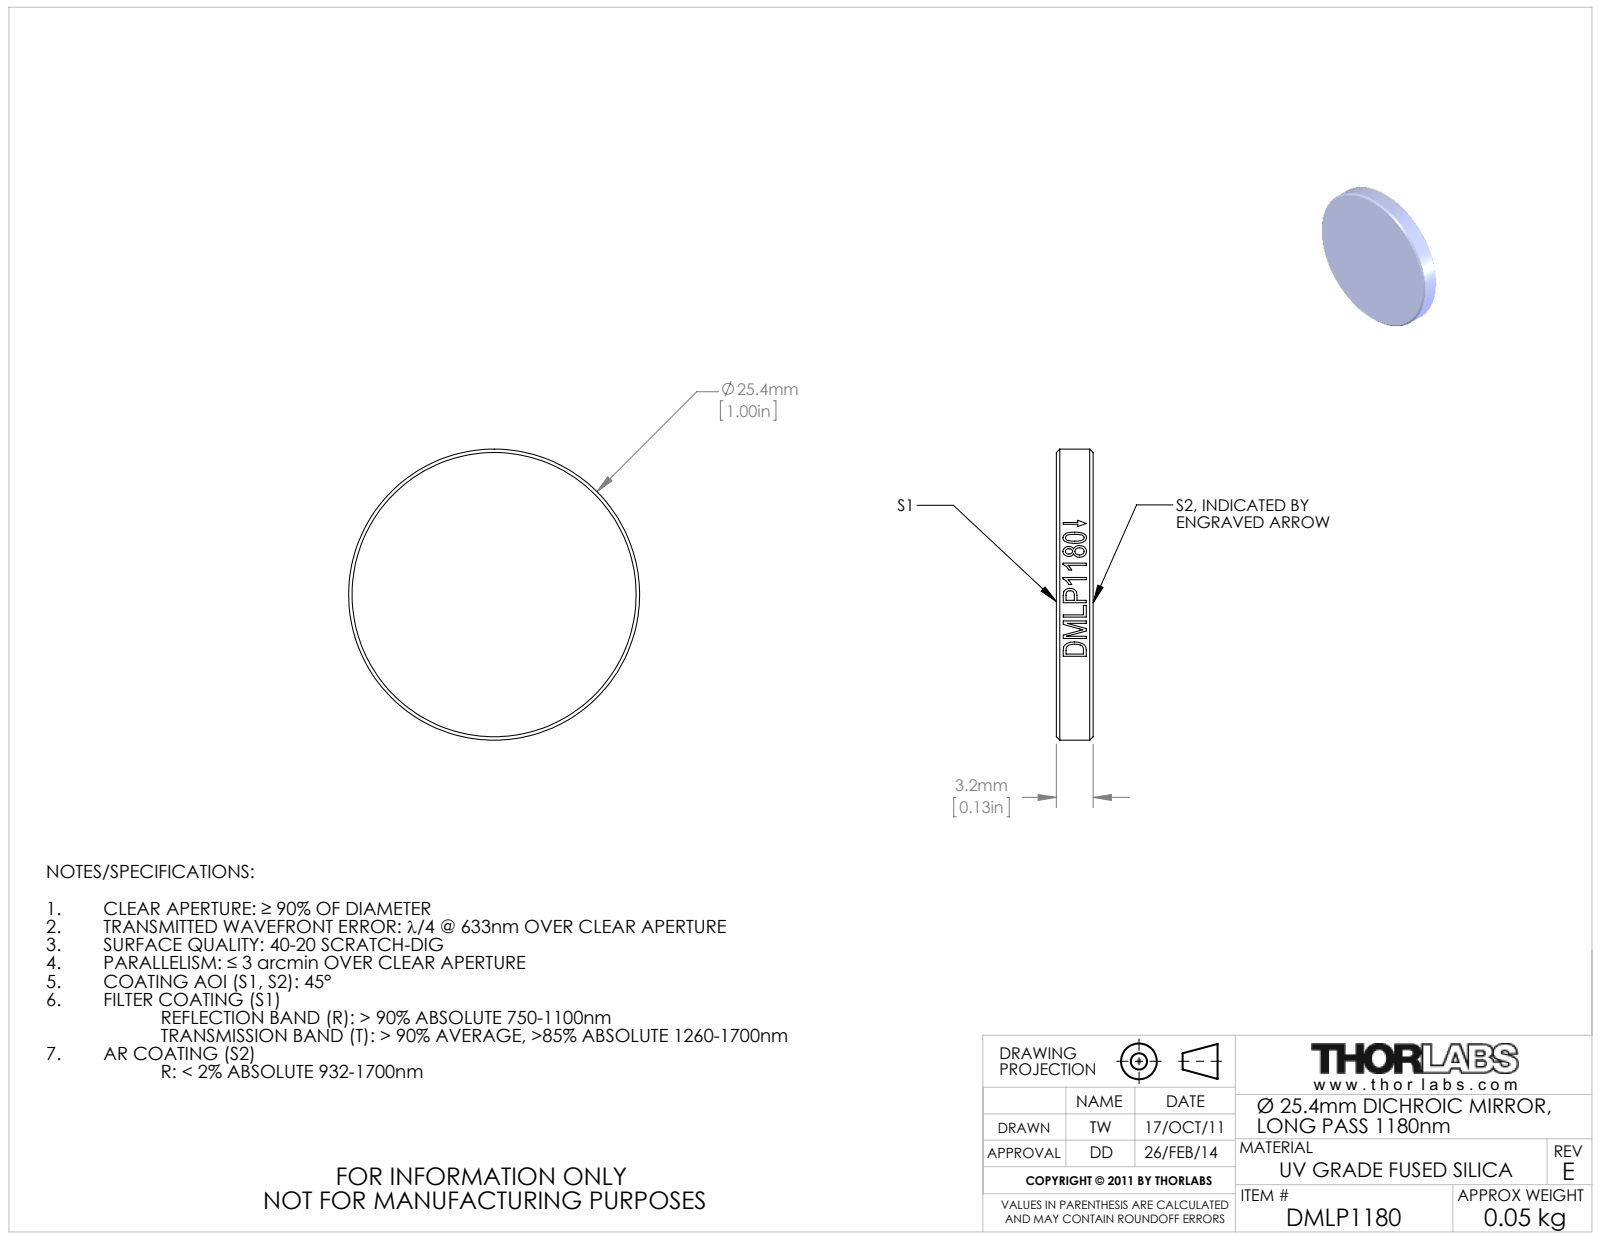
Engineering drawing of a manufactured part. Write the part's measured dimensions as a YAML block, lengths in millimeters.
part_name: "21637-E0W"
step_written_by: "SolidWorks 2011 (CONFIG_CONTROL_DESIGN)"
units: millimeters
bodies: {solids: 0, faces: 22, planar: 2, cylindrical: 16, other: 4}
overall_size: [25.4, 25.4, 3.2]
round_bosses_or_shafts:
  - {diameter: 25.4, count: 1}
face_to_face_distances: [3.2]
